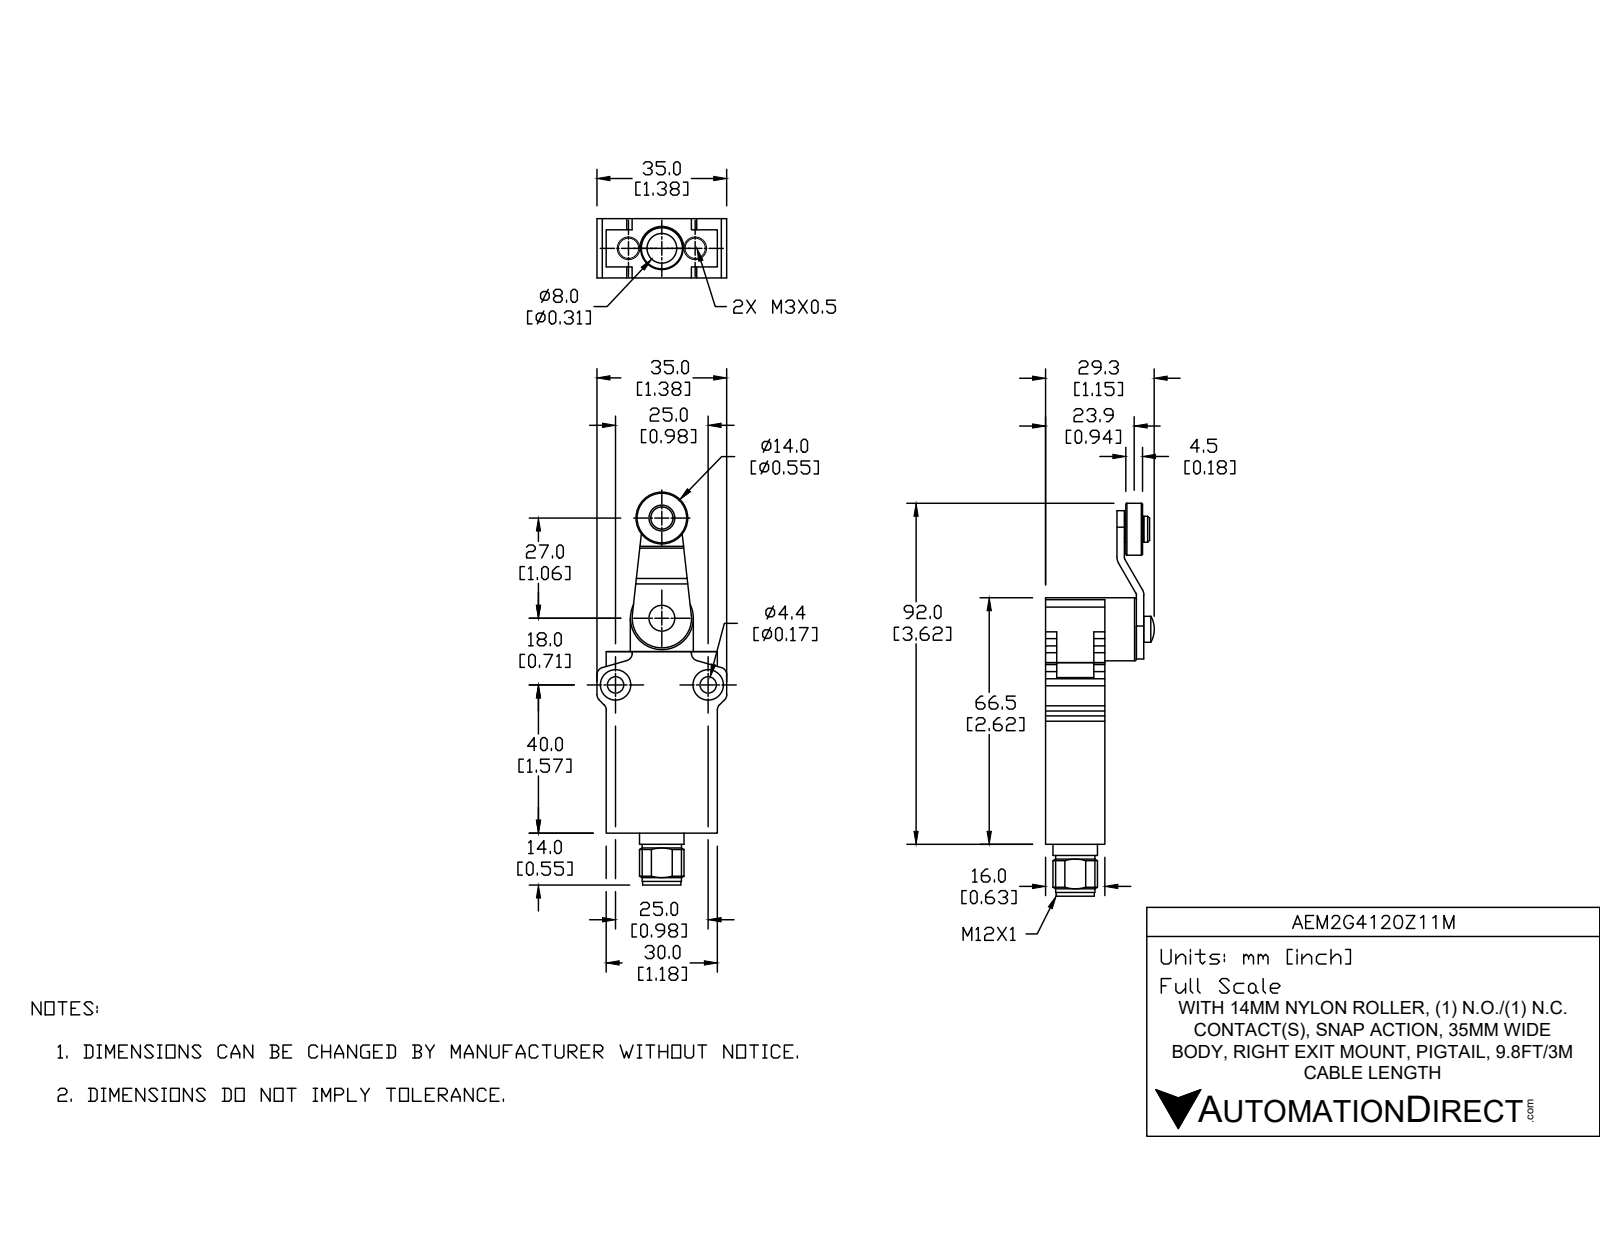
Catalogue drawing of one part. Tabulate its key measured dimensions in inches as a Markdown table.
| quantity | value |
| --- | --- |
| part name | AEM2G4120Z11M |
| STEP written by | SolidWorks 2017 (AUTOMOTIVE_DESIGN) |
| units | inches |
| bodies | 6 solids, 594 faces (300 planar, 93 cylindrical, 201 other) |
| overall size | 4.272 × 1.378 × 1.26 |
| volume | 1.981 in³ |
| surface area | 18.28 in² |
| round holes (diameter × count) | 0.118 × 2, 0.173 × 2, 0.323 × 2, 0.098 × 1, 0.138 × 1, 0.161 × 1, 0.197 × 1, 0.224 × 1 |
| round bosses / shafts (diameter × count) | 0.276 × 2, 0.622 × 1, 0.551 × 1, 0.472 × 1, 0.417 × 1, 0.406 × 1, 0.394 × 1, 0.236 × 1 |
| partial cylindrical surfaces (radius × count) | 0.079 × 8, 0.039 × 2, 0.118 × 2, 0.256 × 1, 0.315 × 1 |
| main face-to-face distances | 0.63, 1.181, 0.354, 0.079, 2.047, 0.984, 0.102, 0.472, 0.433, 0.898 |
| hole center spacings | 0.748, 0.861, 0.865, 0.984, 1.043, 1.819, 1.821 |
